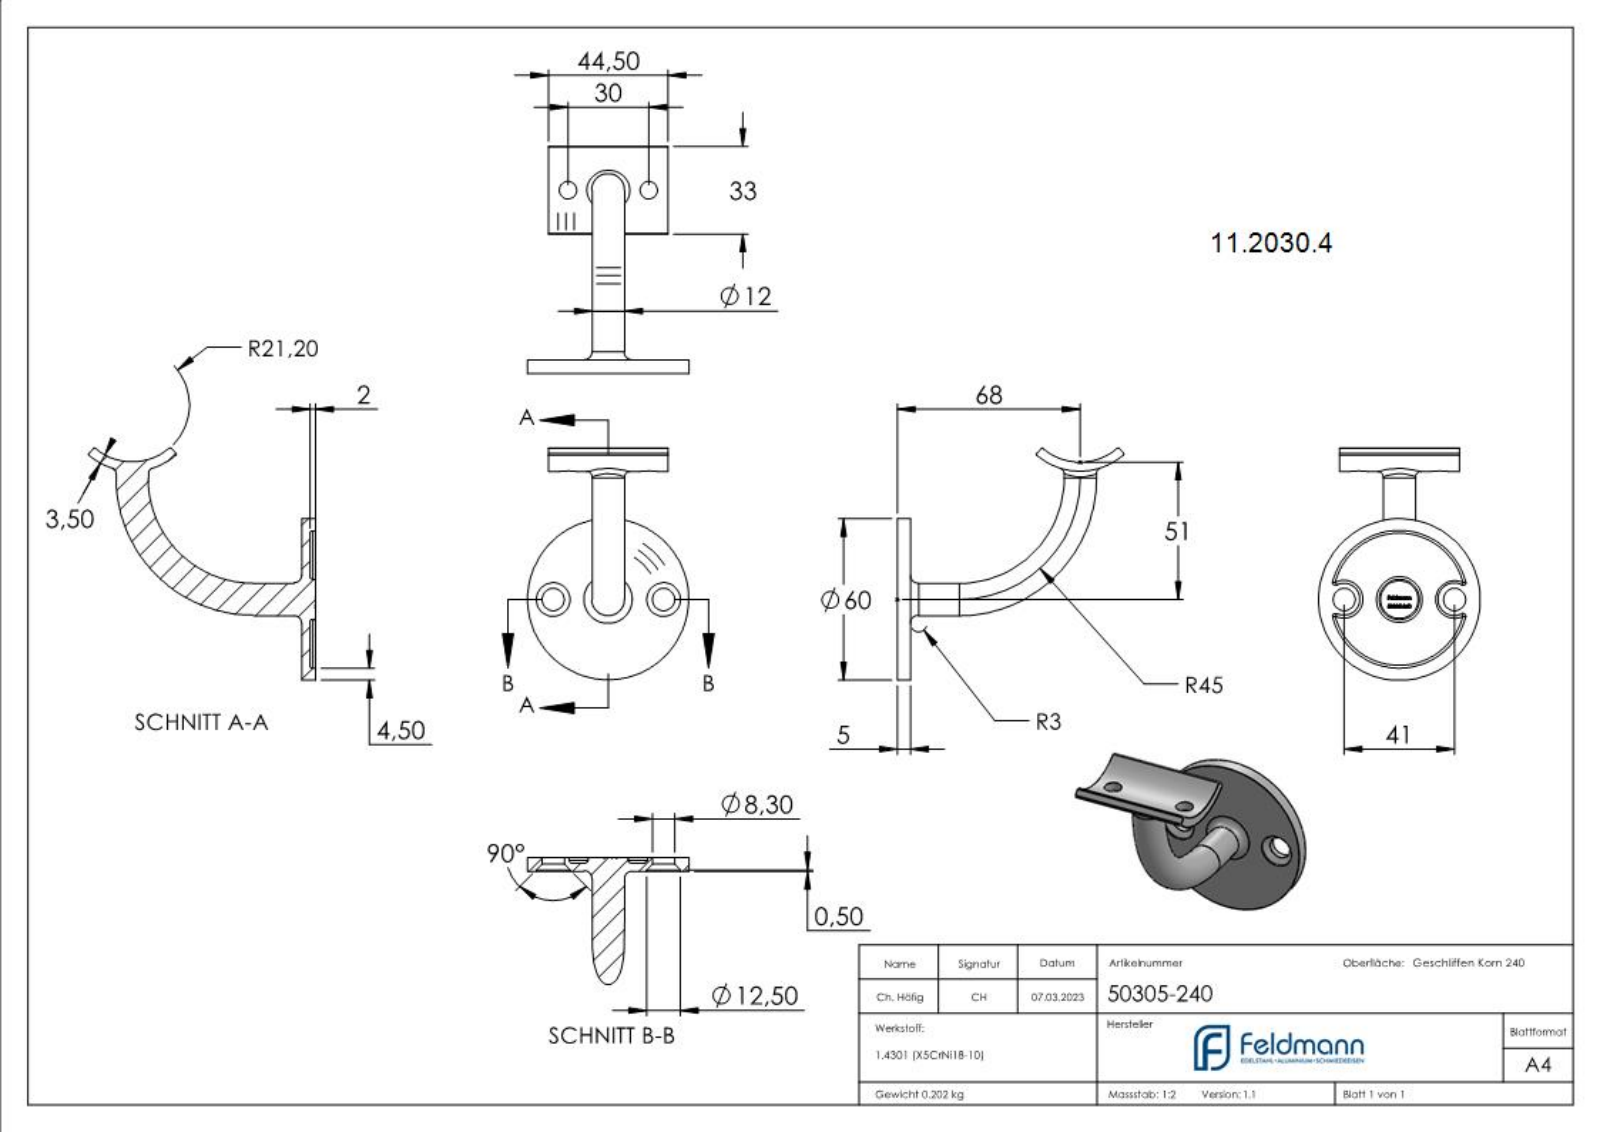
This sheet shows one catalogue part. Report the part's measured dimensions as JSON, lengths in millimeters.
{"part_name": "50305-240", "step_written_by": "SolidWorks 2018 (CONFIG_CONTROL_DESIGN)", "units": "millimeters", "bodies": {"solids": 1, "faces": 274, "planar": 124, "cylindrical": 24, "other": 126}, "overall_size": [86.22, 84.29, 60], "volume_mm3": 25581, "surface_area_mm2": 13643, "round_holes": [[6.5, 2], [8.3, 2], [12.5, 2], [51, 1]], "round_bosses_or_shafts": [[12, 2], [60, 1], [15, 1]], "partial_cylinders_radius": [[0.5, 4], [1, 4], [6, 2], [21.2, 1], [24.7, 1]], "face_to_face_distances": [3, 2, 5, 44.5, 1.9, 4.9, 2.97, 0.39, 1.32, 4.09], "hole_center_spacings": [20.5, 30, 41]}
